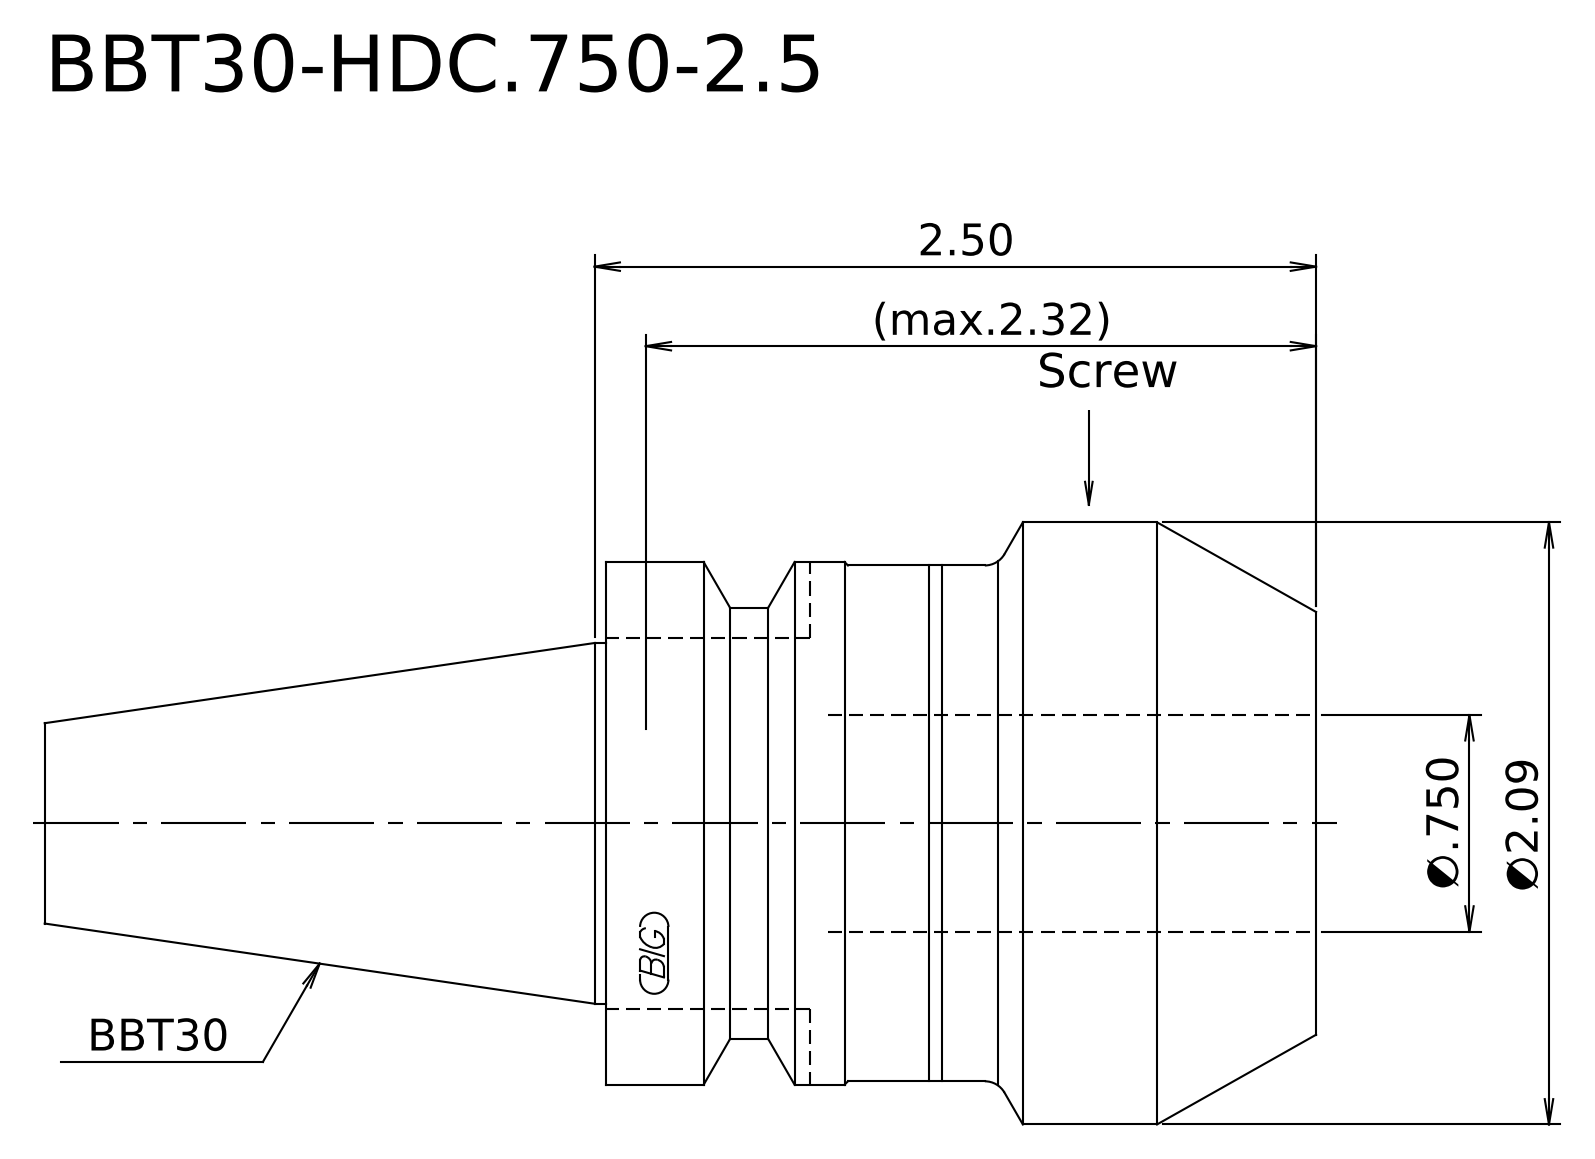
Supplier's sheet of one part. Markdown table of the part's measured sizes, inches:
| quantity | value |
| --- | --- |
| STEP written by | Kubotek KeyCreator 2011 V10.0.2 (22737) (automotive_design) |
| units | inches |
| bodies | 1 solid, 16 faces (3 planar, 6 cylindrical, 7 other) |
| overall size | 4.406 × 2.087 × 2.087 |
| volume | 8.008 in³ |
| surface area | 25.45 in² |
| round bosses / shafts (diameter × count) | 2.087 × 1, 1.811 × 1, 1.787 × 1, 1.496 × 1, 1.25 × 1 |
| main face-to-face distances | 2.461, 4.406, 1.945 |
